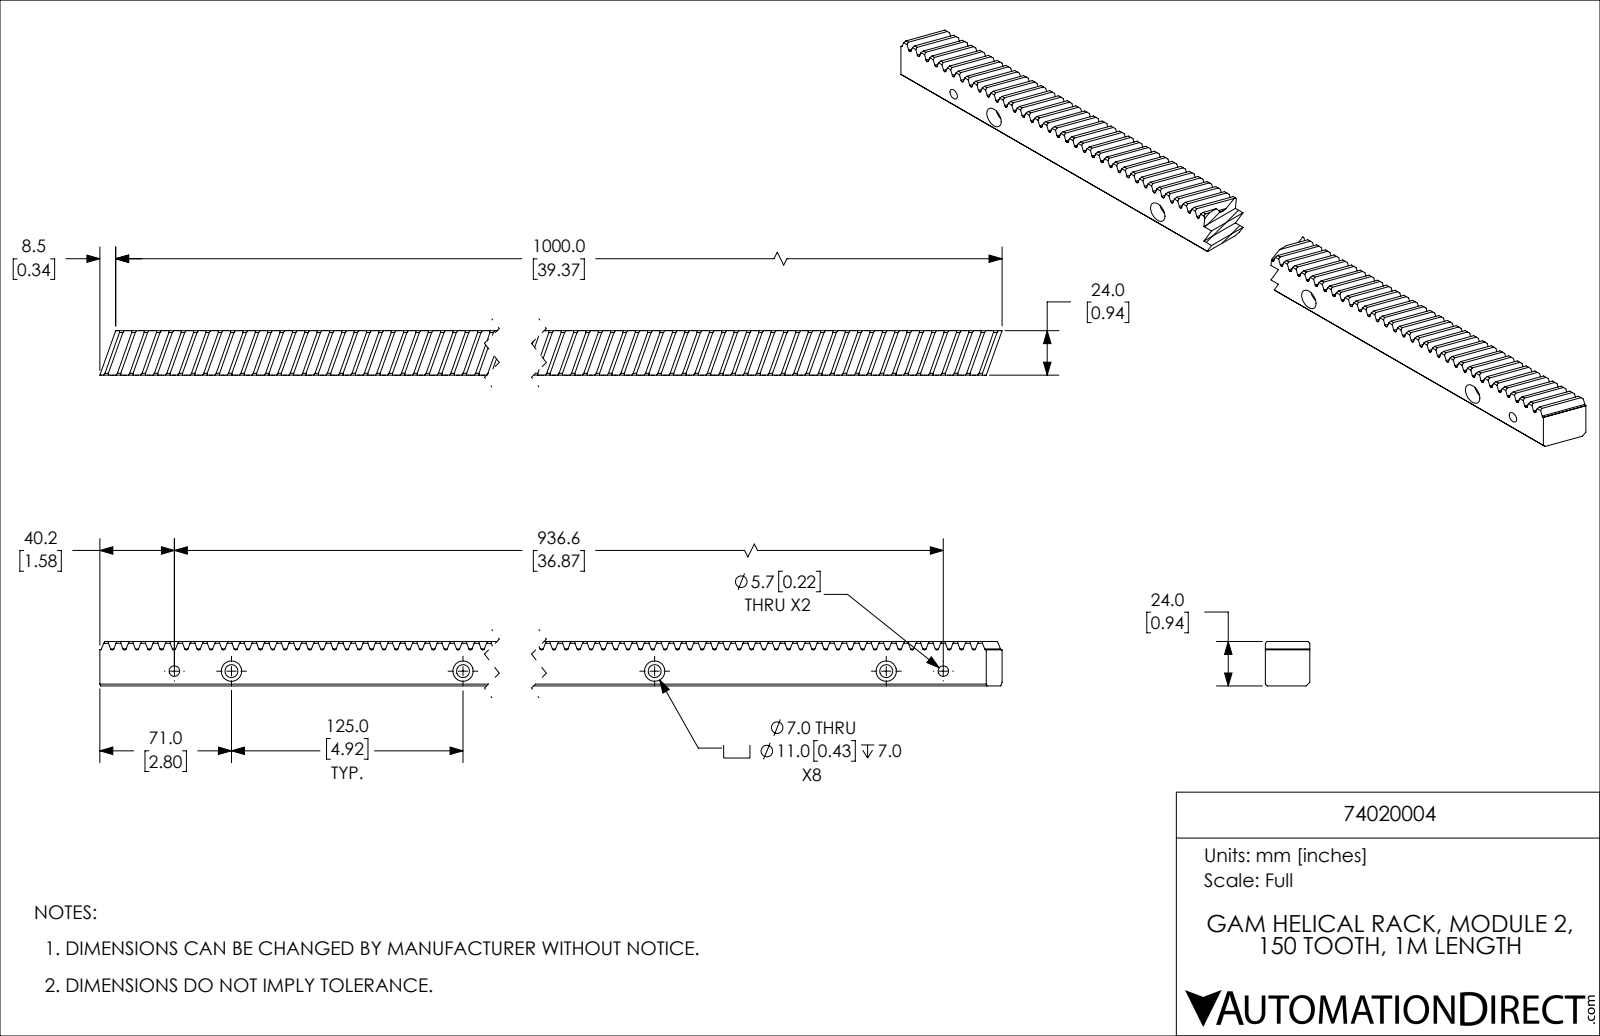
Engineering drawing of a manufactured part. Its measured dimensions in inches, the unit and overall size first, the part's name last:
Units: inches
Overall size (bounding box): 39.705 × 0.945 × 0.945
Round holes (diameter × count): ⌀0.276 ×8, ⌀0.433 ×8, ⌀0.224 ×2
Main face-to-face distances: 0.945, 2.093, 0.768, 0.177, 3.488, 1.395, 0.233, 0.93, 1.628, 1.163
Hole centre spacings: 4.921, 9.843, 14.764, 19.685, 24.606, 1.213, 6.134, 11.055
Volume: 31.24 in³ · Surface area: 183.9 in²
Bodies: 1 solid, 1252 faces (916 planar, 36 cylindrical, 300 other)
Part name (STEP PRODUCT): 74020004
STEP written by: SolidWorks 2019 (CONFIG_CONTROL_DESIGN)
